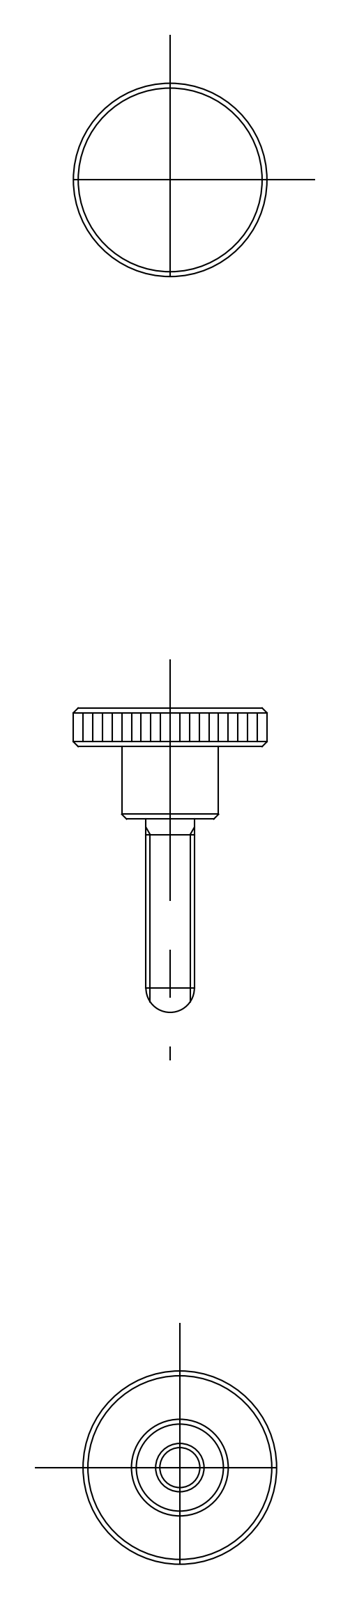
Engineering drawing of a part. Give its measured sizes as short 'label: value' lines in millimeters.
name: knob
written by: CADfix (AUTOMOTIVE_DESIGN)
unit: mm
bodies: 1 solid, 16 faces (0 planar, 0 cylindrical, 16 other)
size: 31.5 × 20 × 20
volume: 2 206 mm³; area: 1 363 mm²
